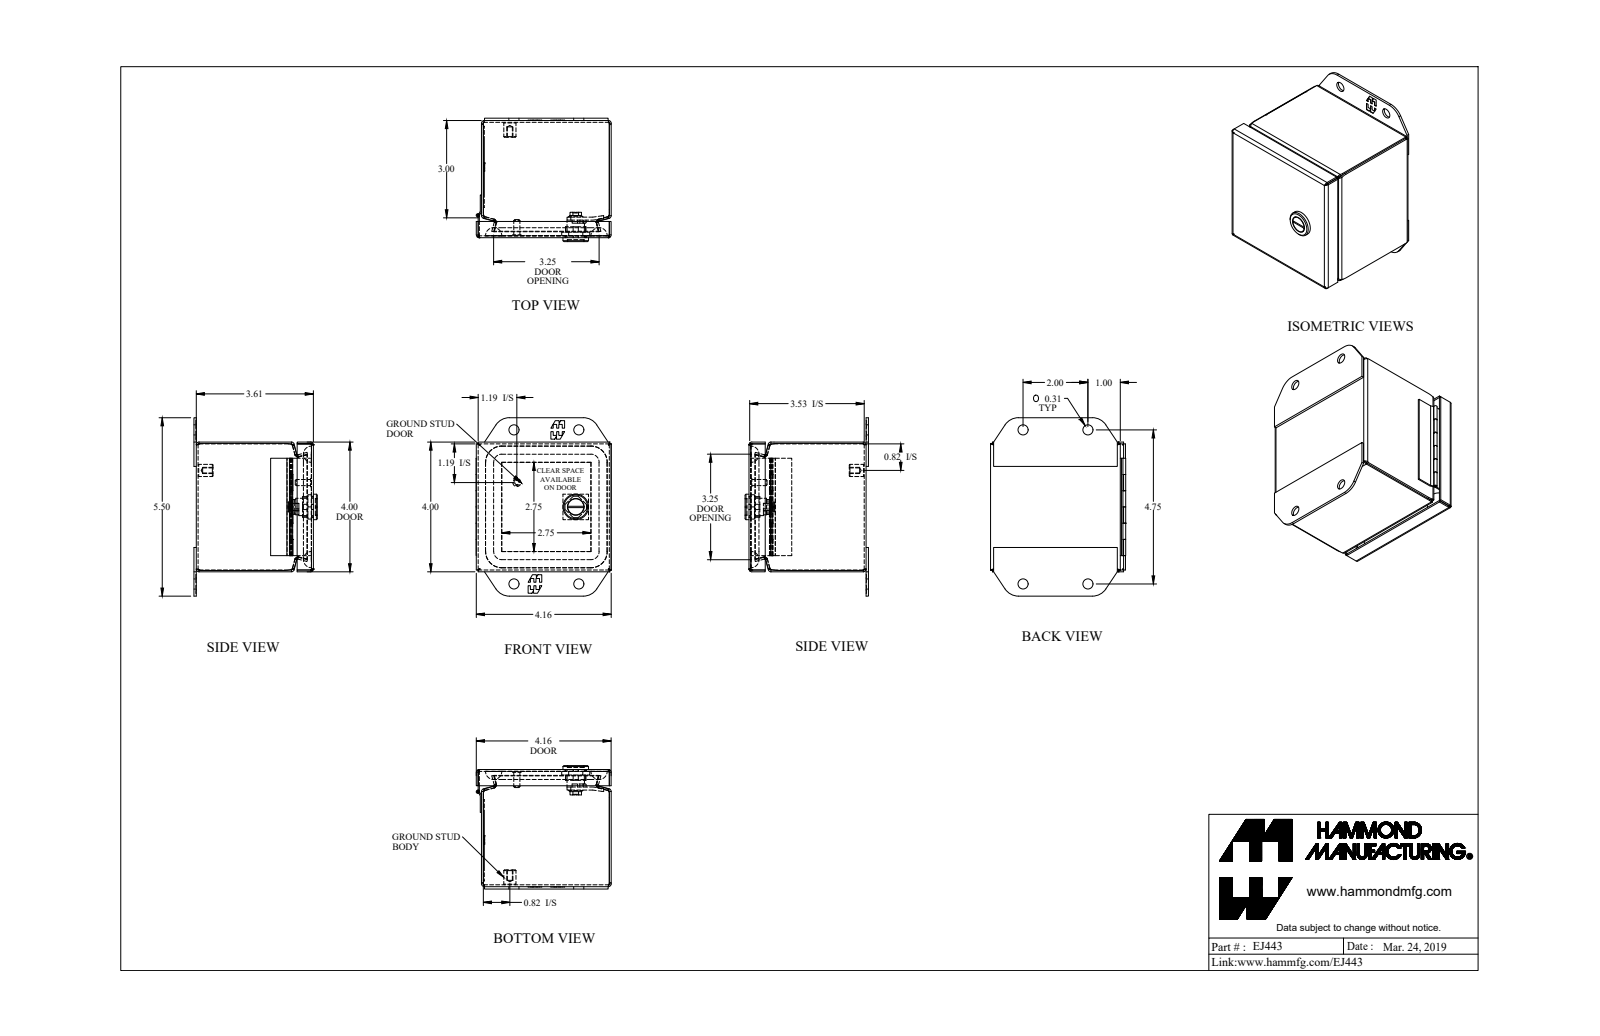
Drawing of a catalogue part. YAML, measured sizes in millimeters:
part_name: "EJ443_Default"
step_written_by: "SolidWorks 2019 (CONFIG_CONTROL_DESIGN)"
units: millimeters
bodies: {solids: 11, faces: 517, planar: 315, cylindrical: 134, other: 68}
overall_size: [139.7, 105.8, 96.6]
volume: 127800
surface_area: 166200
round_holes:
  - {diameter: 8, count: 4}
  - {diameter: 1.3, count: 1}
  - {diameter: 4, count: 1}
  - {diameter: 13.1, count: 1}
round_bosses_or_shafts:
  - {diameter: 20, count: 1}
  - {diameter: 13.6, count: 1}
  - {diameter: 12.6, count: 1}
  - {diameter: 11, count: 1}
  - {diameter: 9.5, count: 1}
  - {diameter: 6.4, count: 1}
  - {diameter: 4.8, count: 1}
  - {diameter: 2.5, count: 1}
partial_cylinders:
  - {radius: 0.7, count: 16}
  - {radius: 2.2, count: 16}
  - {radius: 7.1, count: 10}
  - {radius: 6.4, count: 4}
  - {radius: 12.7, count: 4}
  - {radius: 12.7, count: 4}
  - {radius: 1.5, count: 2}
  - {radius: 13.7, count: 2}
face_to_face_distances: [1.4, 100.2, 98.7, 101.6, 90.3, 1.4, 91.7, 90.3, 88.8, 93.5]
hole_center_spacings: [50.8, 60.4, 77.4, 120.7, 130.9, 31.9, 59, 62.6]
